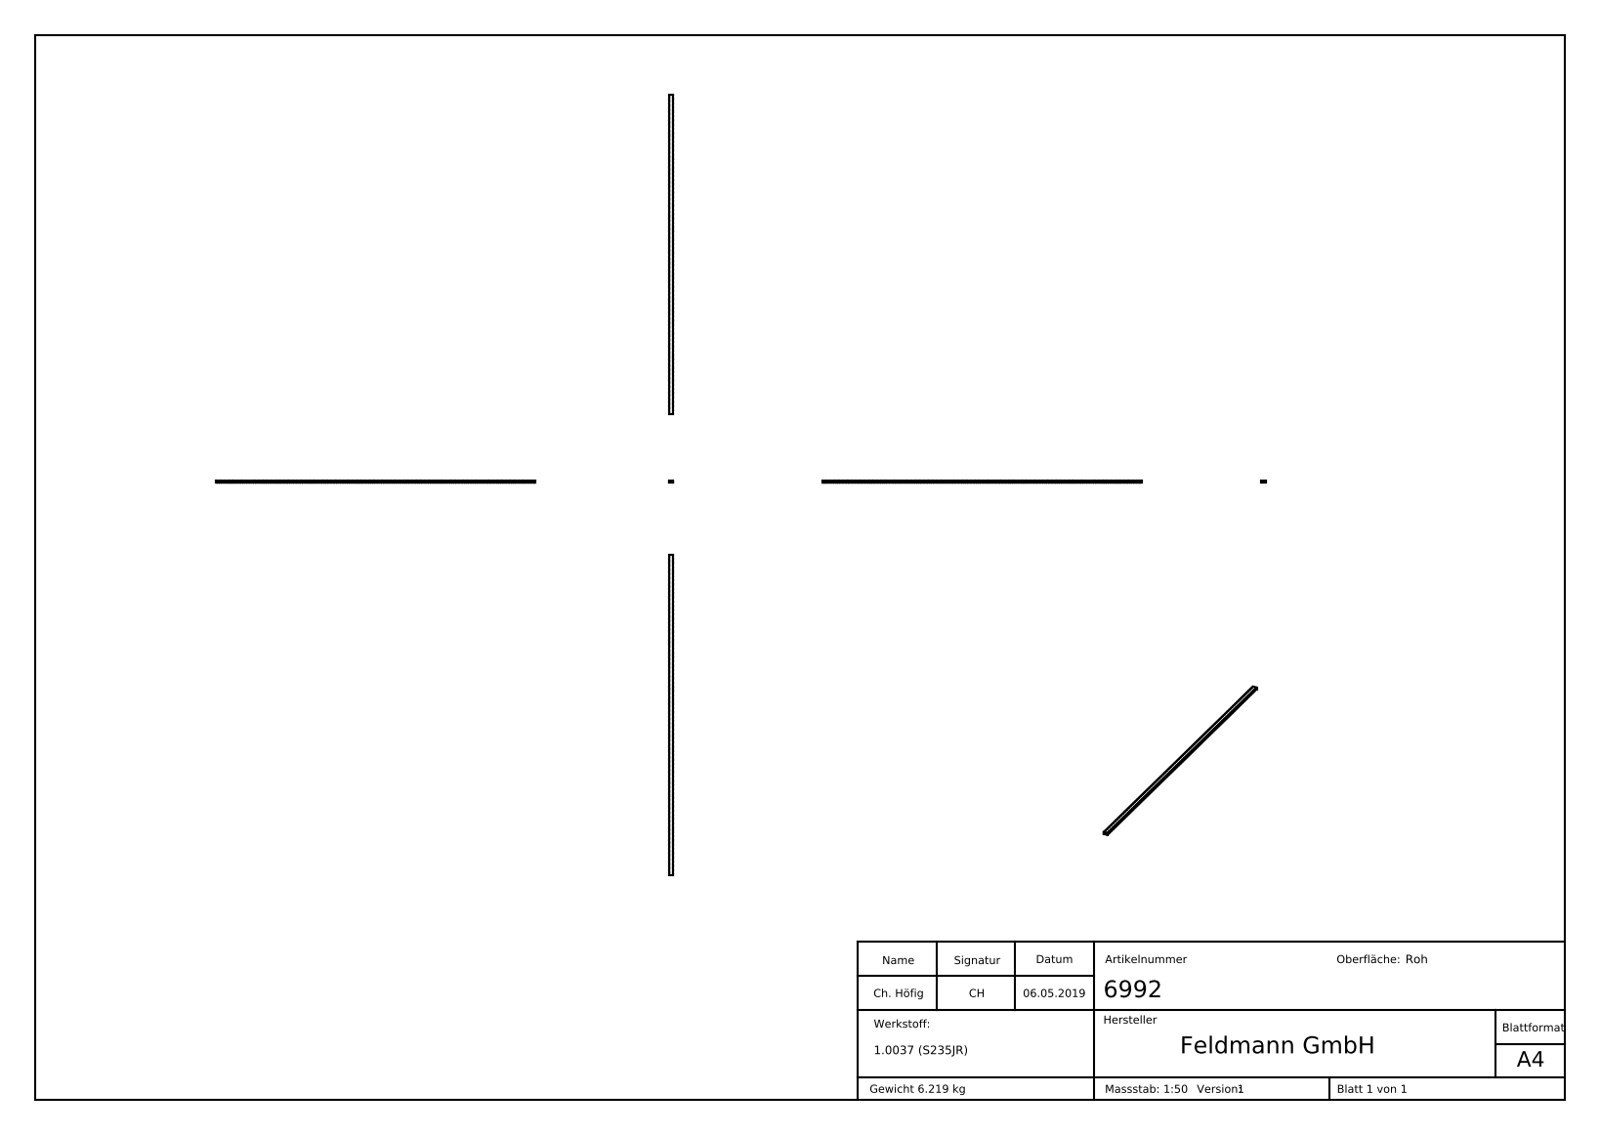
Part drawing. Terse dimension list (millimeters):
name: 6992
written by: SolidWorks 2018 (CONFIG_CONTROL_DESIGN)
unit: mm
bodies: 1 solid, 2390 faces (99 planar, 1106 cylindrical, 1185 other)
size: 3000 × 40 × 20
volume: 642 435 mm³; area: 648 429 mm²
rounds: 4× R1, 4× R3
face distances: 2, 18, 20, 16, 38, 40, 36, 3000, 2500, 500
